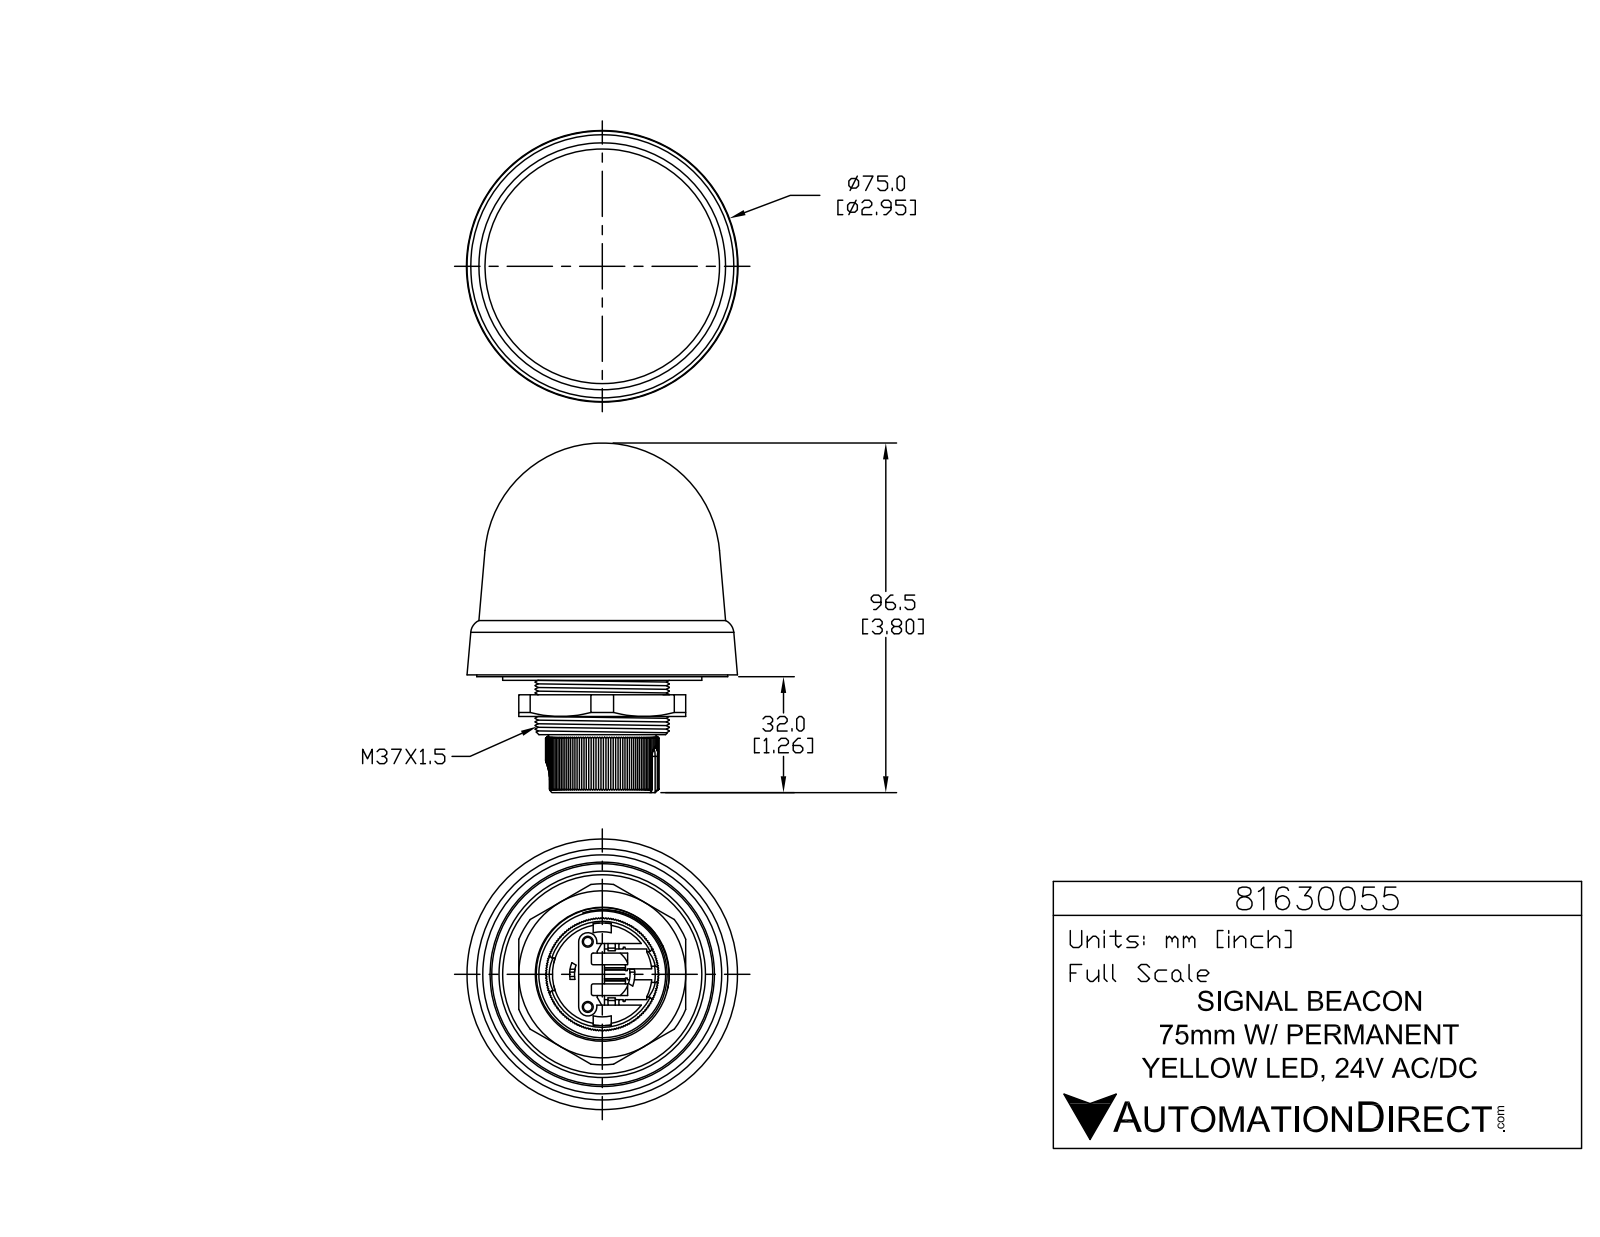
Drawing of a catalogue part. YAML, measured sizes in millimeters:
part_name: "81630055"
step_written_by: "SolidWorks 2019 (CONFIG_CONTROL_DESIGN)"
units: millimeters
bodies: {solids: 3, faces: 560, planar: 432, cylindrical: 80, other: 48}
overall_size: [96.5, 74.7, 74.7]
volume: 202500
surface_area: 37860
round_holes:
  - {diameter: 2.4, count: 2}
  - {diameter: 3, count: 2}
  - {diameter: 15.3, count: 1}
  - {diameter: 29, count: 1}
round_bosses_or_shafts:
  - {diameter: 5.5, count: 2}
  - {diameter: 1.7, count: 2}
  - {diameter: 55, count: 1}
  - {diameter: 37, count: 1}
  - {diameter: 23.5, count: 1}
partial_cylinders:
  - {radius: 0.2, count: 6}
  - {radius: 1, count: 6}
  - {radius: 0.5, count: 4}
  - {radius: 0.8, count: 2}
  - {radius: 2, count: 2}
  - {radius: 2.5, count: 2}
  - {radius: 4.5, count: 1}
  - {radius: 9, count: 1}
face_to_face_distances: [4.5, 9, 5, 11, 13, 8.5, 1.5, 10, 3, 4]
hole_center_spacings: [9.9, 18]
